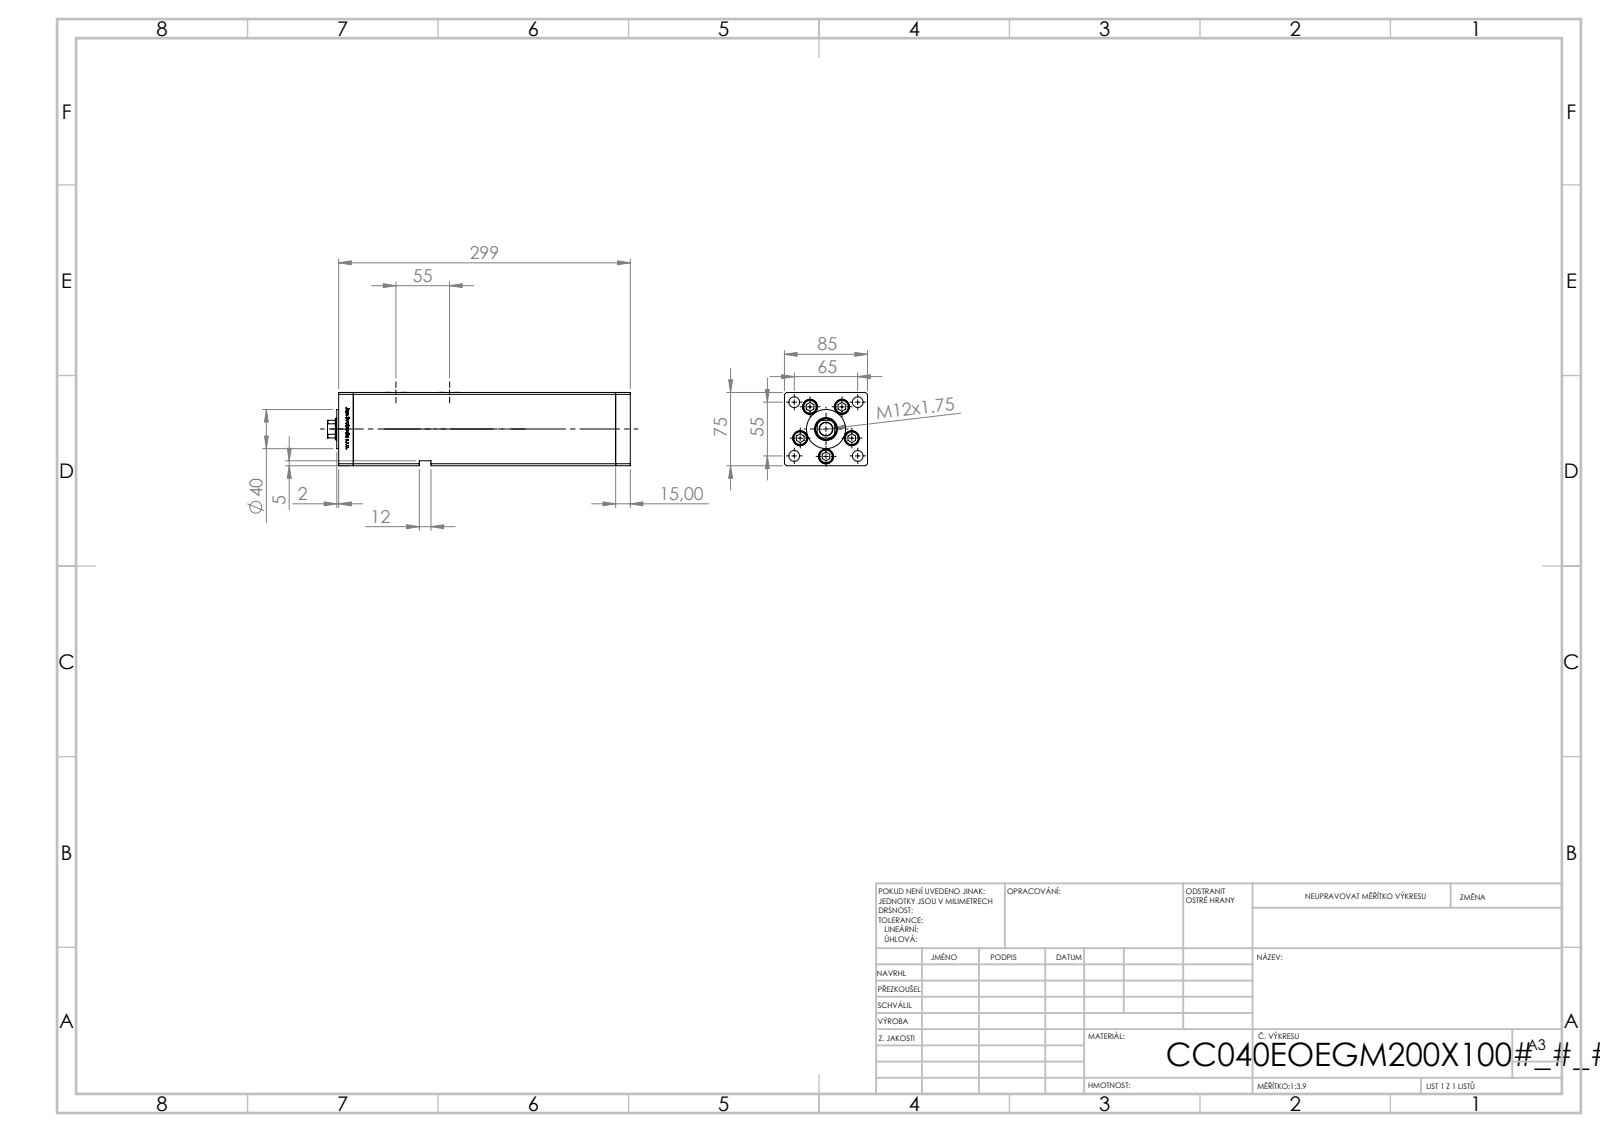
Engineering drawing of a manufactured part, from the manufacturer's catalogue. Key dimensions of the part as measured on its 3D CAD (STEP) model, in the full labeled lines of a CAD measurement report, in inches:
Part name (STEP PRODUCT): V220C BACK_E; V220C_VC_E; ALLEN BOLT; V220C_E MIDDLE (+1 more)
STEP written by: SolidWorks 2019 (CONFIG_CONTROL_DESIGN)
Units: inches
Bodies: 14 solids, 1214 faces (475 planar, 165 cylindrical, 574 other)
Overall size (bounding box): 12.205 × 3.346 × 2.953
Volume: 98 in³ · Surface area: 366.3 in²
Round holes (diameter × count): ⌀0.433 ×9, ⌀0.61 ×5, ⌀0.413 ×4, ⌀0.65 ×4, ⌀0.079 ×2, ⌀0.518 ×2, ⌀0.531 ×1, ⌀0.866 ×1, ⌀0.925 ×1
Round bosses / shafts (diameter × count): ⌀0.571 ×5, ⌀0.315 ×5, ⌀1.575 ×1
Partial cylindrical surfaces — rounded edges, fillets, slot ends (radius × count): R0.037 ×2, R0.413 ×1
Main face-to-face distances: 3.346, 2.953, 0.591, 10.571, 11.161, 0.413, 2.539, 11.752, 2.697, 1.23
Hole centre spacings: 1.102, 1.676, 2.165, 2.559, 3.352, 0.664, 0.755, 1.273
